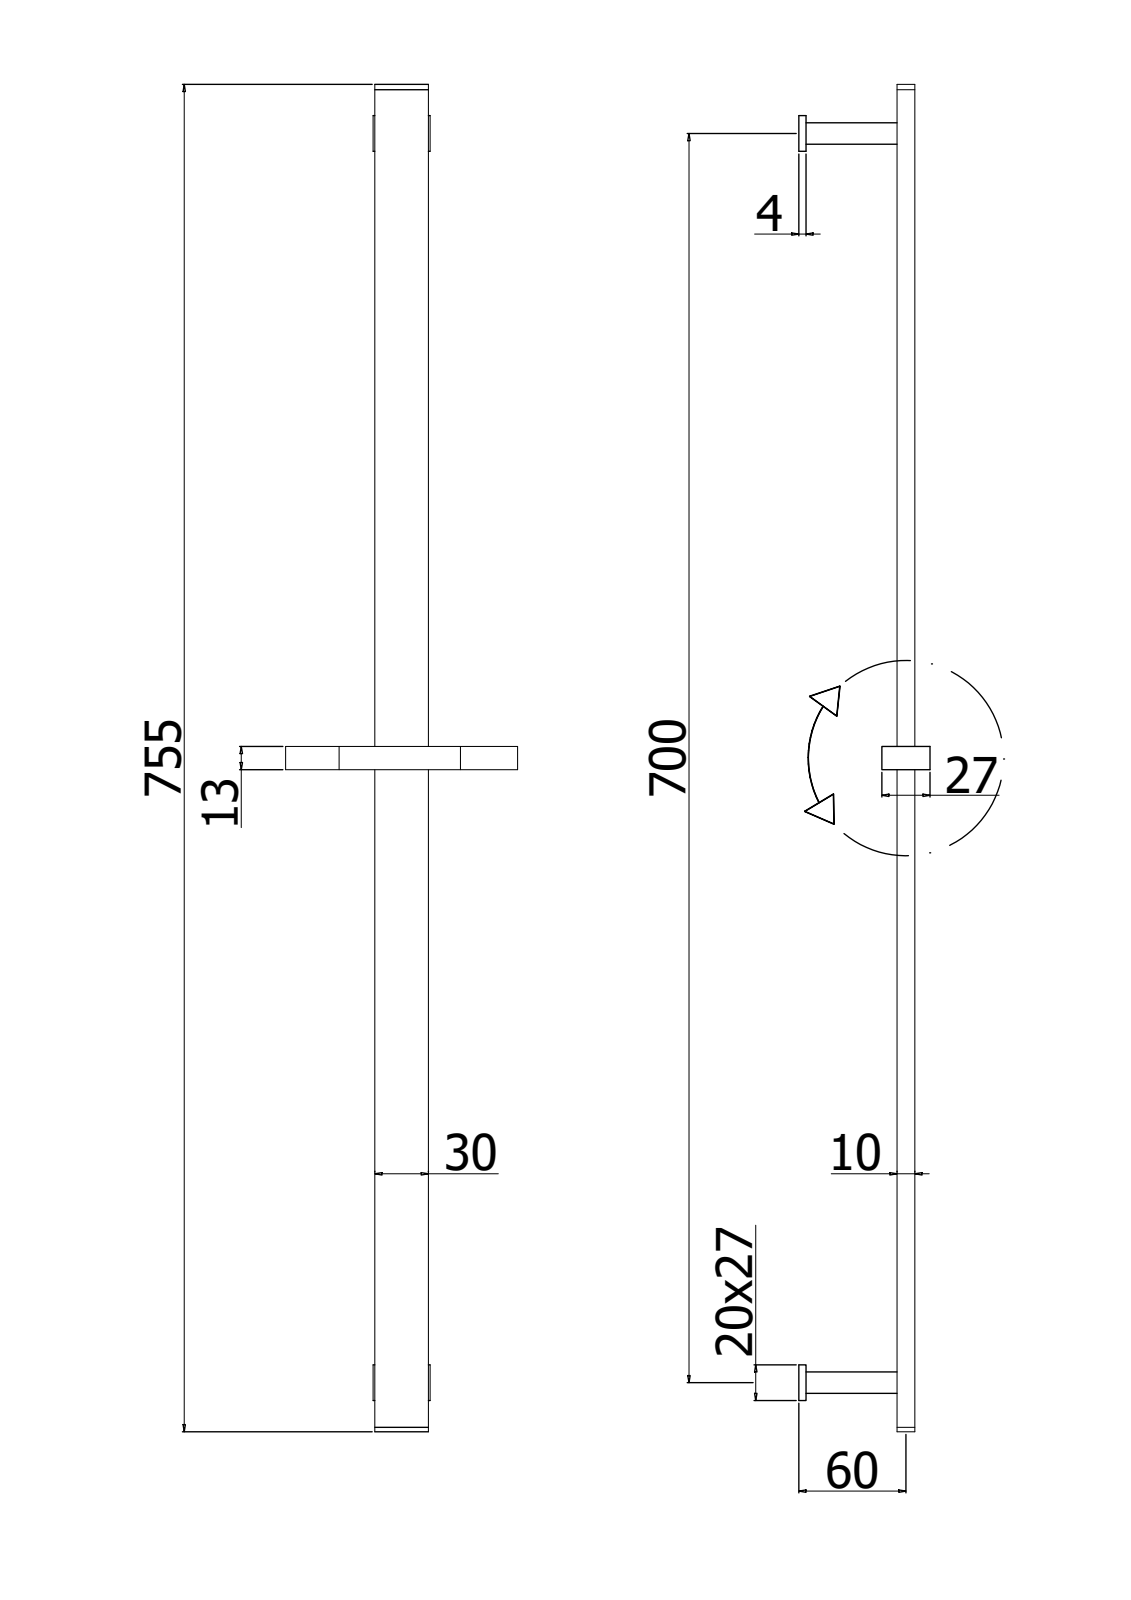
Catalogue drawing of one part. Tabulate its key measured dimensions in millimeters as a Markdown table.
| quantity | value |
| --- | --- |
| part name | ZSAL117CR |
| STEP written by | CREO PARAMETRIC BY PTC INC, 2020044 (CONFIG_CONTROL_DESIGN) |
| units | millimeters |
| bodies | 0 solids, 105 faces (61 planar, 39 cylindrical, 5 other) |
| overall size | 906.4 × 131 × 73.75 |
| partial cylindrical surfaces (radius × count) | 0.3 × 14, 0.2 × 10 |
| main face-to-face distances | 10, 30, 27.5, 8.75, 18.75, 13.5, 850, 12, 2.5, 46.25 |
